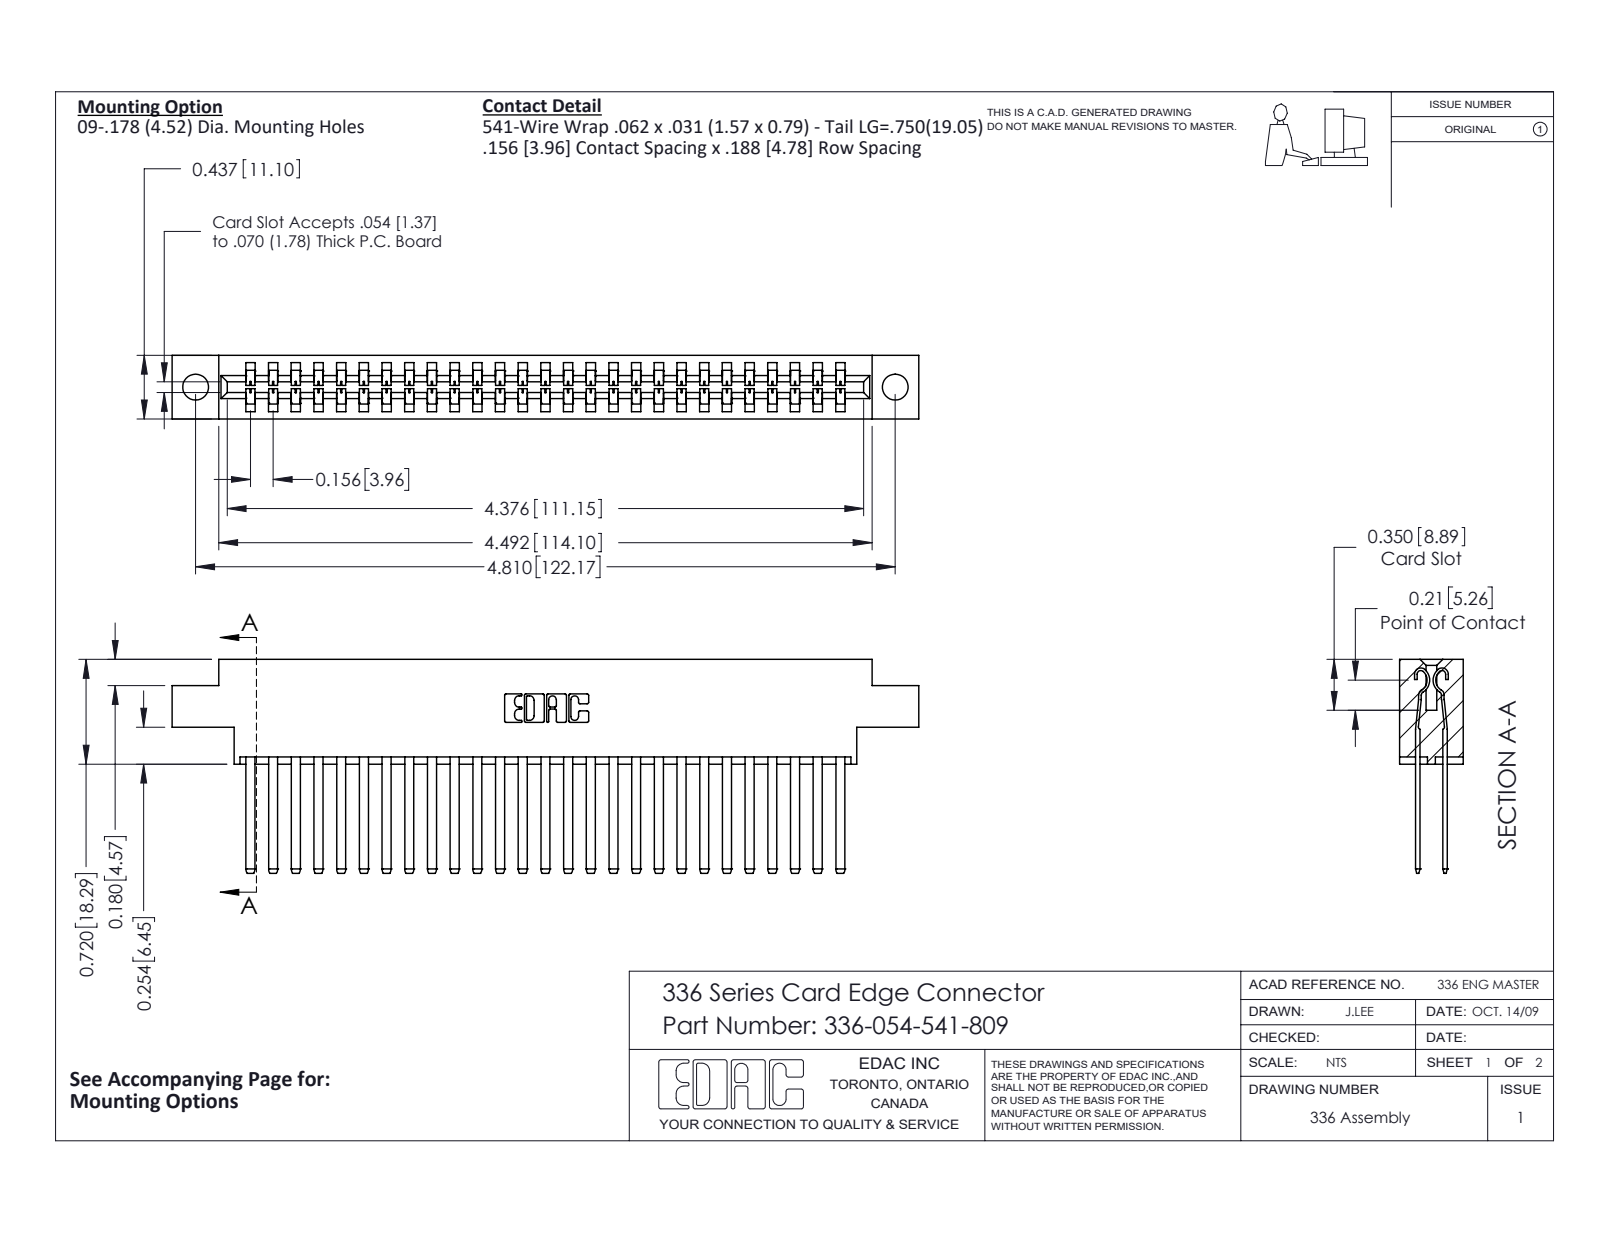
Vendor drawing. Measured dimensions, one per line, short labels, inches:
name: 336-054-541-809; 336 Part_Offset - .178 Dia - TH; 336-290-001_336-290-541
written by: SolidWorks 2020 (CONFIG_CONTROL_DESIGN)
unit: in
bodies: 55 solids, 2386 faces (1478 planar, 908 cylindrical, 0 other)
size: 5.133 × 1.47 × 0.437
volume: 1.191 in³; area: 38.2 in²
holes: 2× ⌀0.178
rounds: 108× R0.004, 54× R0.056, 22× R0.01, 6× R0.007, 6× R0.031, 4× R0.022, 4× R0.04, 3× R0.026
face distances: 0.188, 0.328, 0.14, 0.297, 0.109, 0.031, 0.437, 0.033, 0.181, 0.256
hole spacings: 4.81
